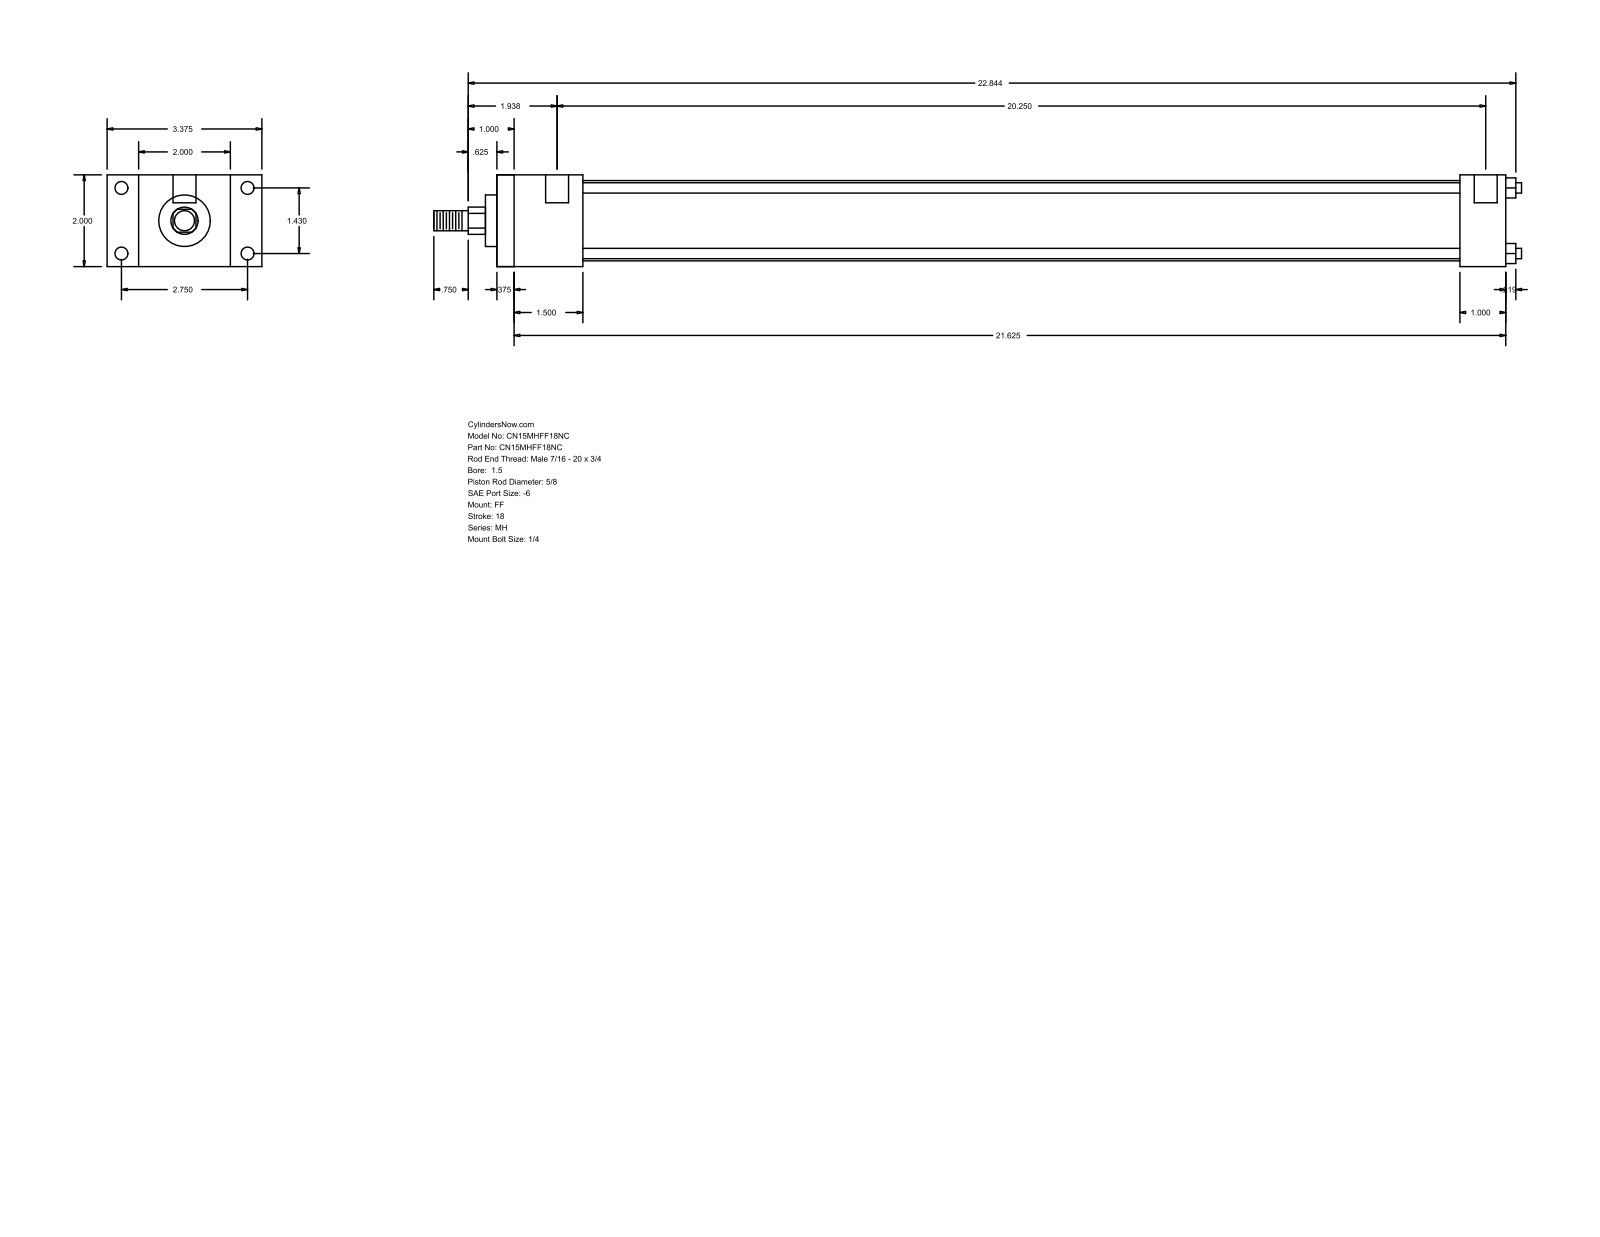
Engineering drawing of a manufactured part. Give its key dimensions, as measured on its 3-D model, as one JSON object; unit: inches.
{"part_name": "MH_FF__0150_0.625", "step_written_by": "GSSL Pune (CONFIG_CONTROL_DESIGN)", "units": "inches", "bodies": {"solids": 0, "faces": 92, "planar": 64, "cylindrical": 28, "other": 0}, "overall_size": [23.719, 3.375, 2], "round_holes": [[0.219, 4], [0.281, 4], [0.5, 2]], "round_bosses_or_shafts": [[0.225, 4], [1.75, 1], [1.125, 1], [0.625, 1], [0.437, 1]], "partial_cylinders_radius": [[0.297, 1]], "face_to_face_distances": [2, 22, 21.625, 0.375, 1, 0.687, 2.687, 1.875, 1.5, 20.125], "hole_center_spacings": [1.43, 2.75, 3.099, 20.375, 0.125, 20.25]}
